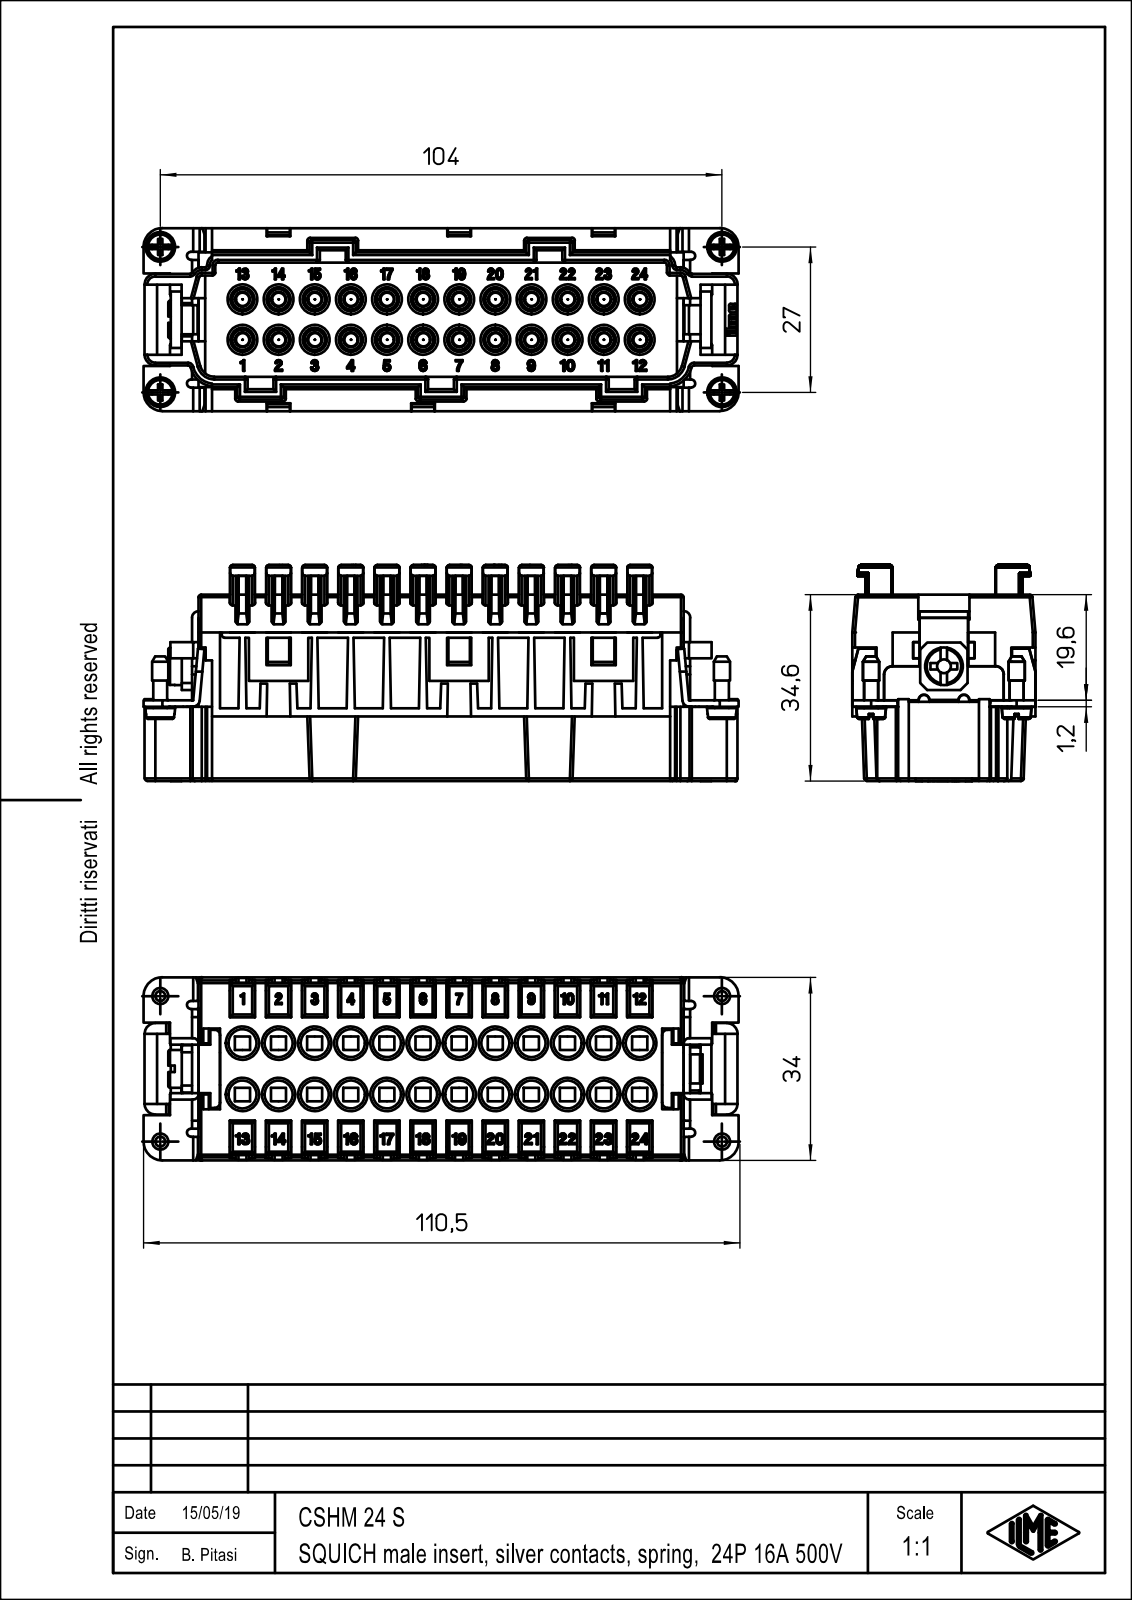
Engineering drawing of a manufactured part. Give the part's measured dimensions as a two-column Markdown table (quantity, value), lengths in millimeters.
| quantity | value |
| --- | --- |
| part name | CSHM_24_S |
| STEP written by | Creo Elements/Direct Modeling 20.1B 02-Apr-2019 (C) Parametric Technology GmbH (AUTOMOTIVE_DESIGN) |
| units | millimeters |
| bodies | 1 solid, 2520 faces (1710 planar, 490 cylindrical, 320 other) |
| overall size | 110.4 × 40.1 × 34 |
| volume | 68 737 mm³ |
| surface area | 41 418 mm² |
| round holes (diameter × count) | 5.2 × 24, 2.8 × 4, 2.58 × 1, 4.2 × 1 |
| round bosses / shafts (diameter × count) | 2.48 × 24, 5.5 × 4, 3 × 4, 2.6 × 4, 7 × 1, 6 × 1, 4 × 1 |
| partial cylindrical surfaces (radius × count) | 0.5 × 129, 0.3 × 52, 1.15 × 24, 1 × 12, 2 × 10, 1.2 × 6, 0.75 × 4, 3.5 × 4 |
| main face-to-face distances | 4.9, 26.1, 1.5, 20.1, 27.6, 6.4, 1, 25.1, 32.5, 2.3 |
| hole center spacings | 6.7, 11.62, 13.4, 16.43, 20.1, 22.23, 26.8, 28.43 |
